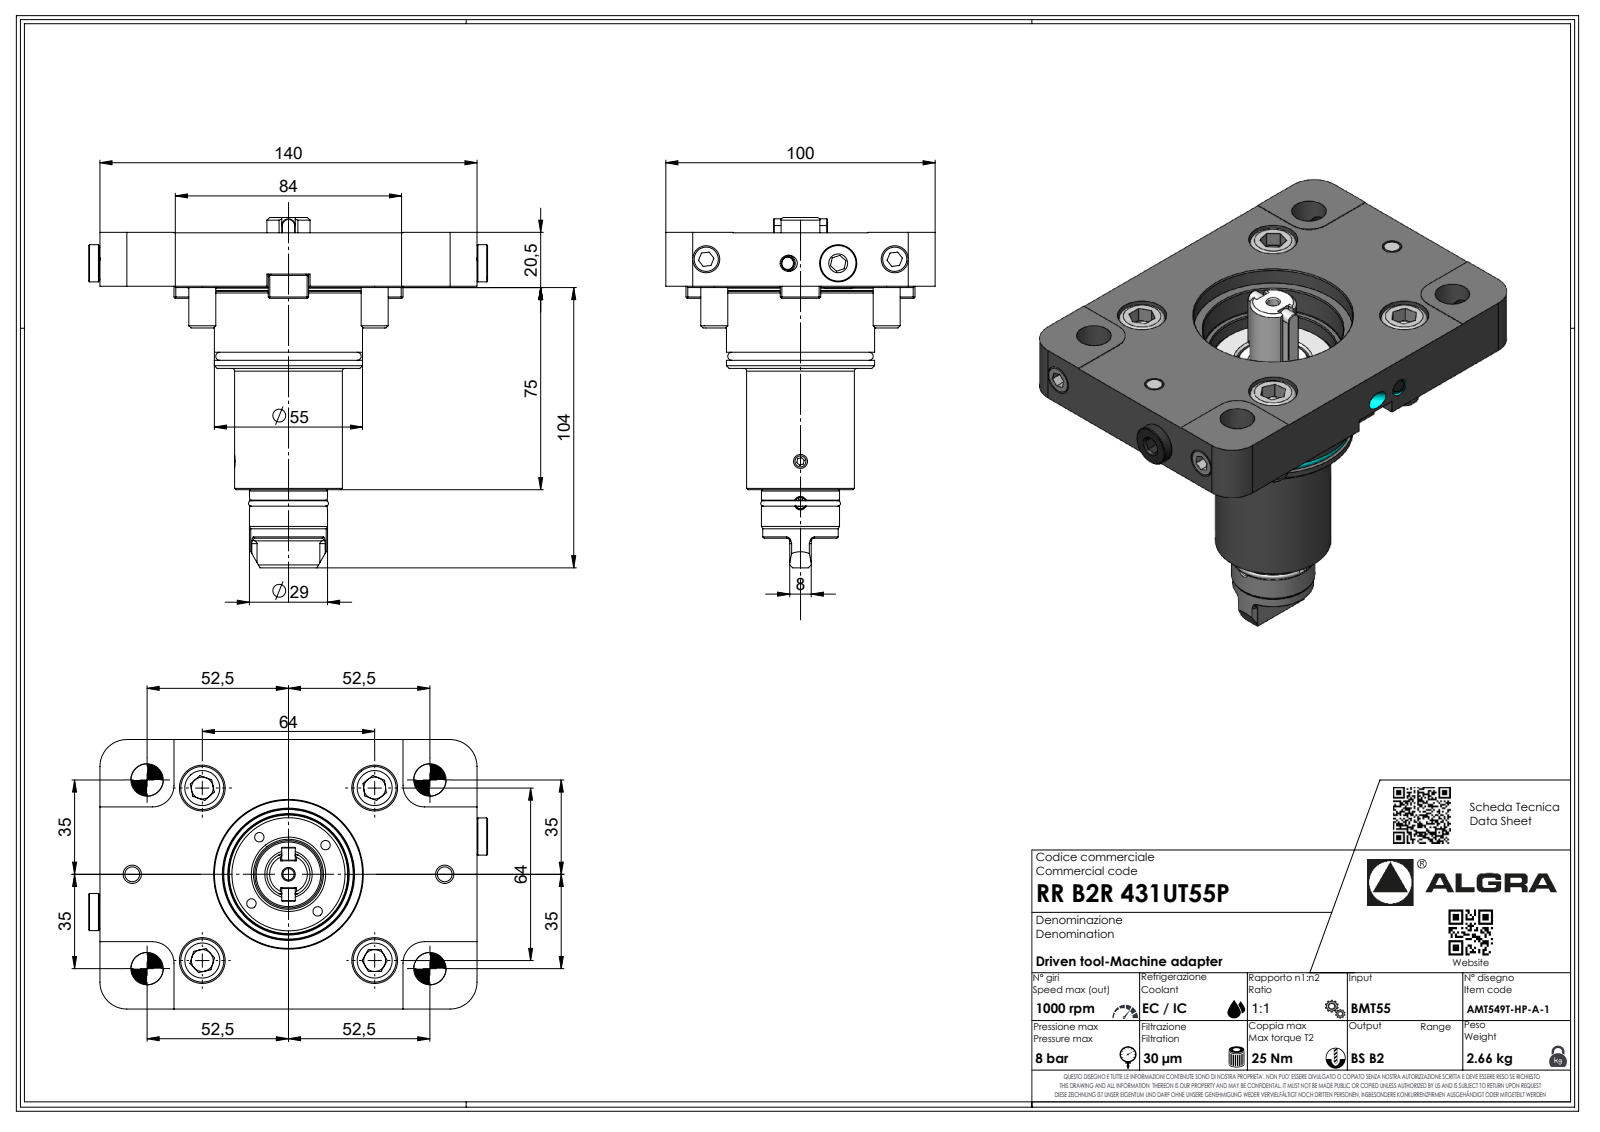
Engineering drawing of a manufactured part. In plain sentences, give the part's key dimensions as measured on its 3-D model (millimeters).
The part is named "RRB2R431UT55P". Its 3-D file was written by "SolidWorks 2023 (AUTOMOTIVE_DESIGN)". It is 1 solid with 514 faces: 334 planar, 86 cylindrical and 94 other. Overall it measures 140 by 130 by 100 millimeters. Its volume is 422 581 cubic millimeters and its surface area 53 368 square millimeters. Round holes: 1 of diameter 2.1. Round bosses or shafts: 1 of diameter 55, 1 of diameter 54.6, 1 of diameter 50.2, 1 of diameter 40, 1 of diameter 29, 1 of diameter 28, 1 of diameter 16, 1 of diameter 6.37. Partial cylindrical surfaces (rounded edges, fillets, slot ends): 12 of radius 2.5, 8 of radius 10, 7 of radius 0.33, 7 of radius 0.52, 7 of radius 3.7, 4 of radius 2, 4 of radius 3, 4 of radius 8. The main face-to-face distances are 19.8, 0.5, 20.3, 20, 20.5, 100, 140, 24.5, 4.5, 30.
